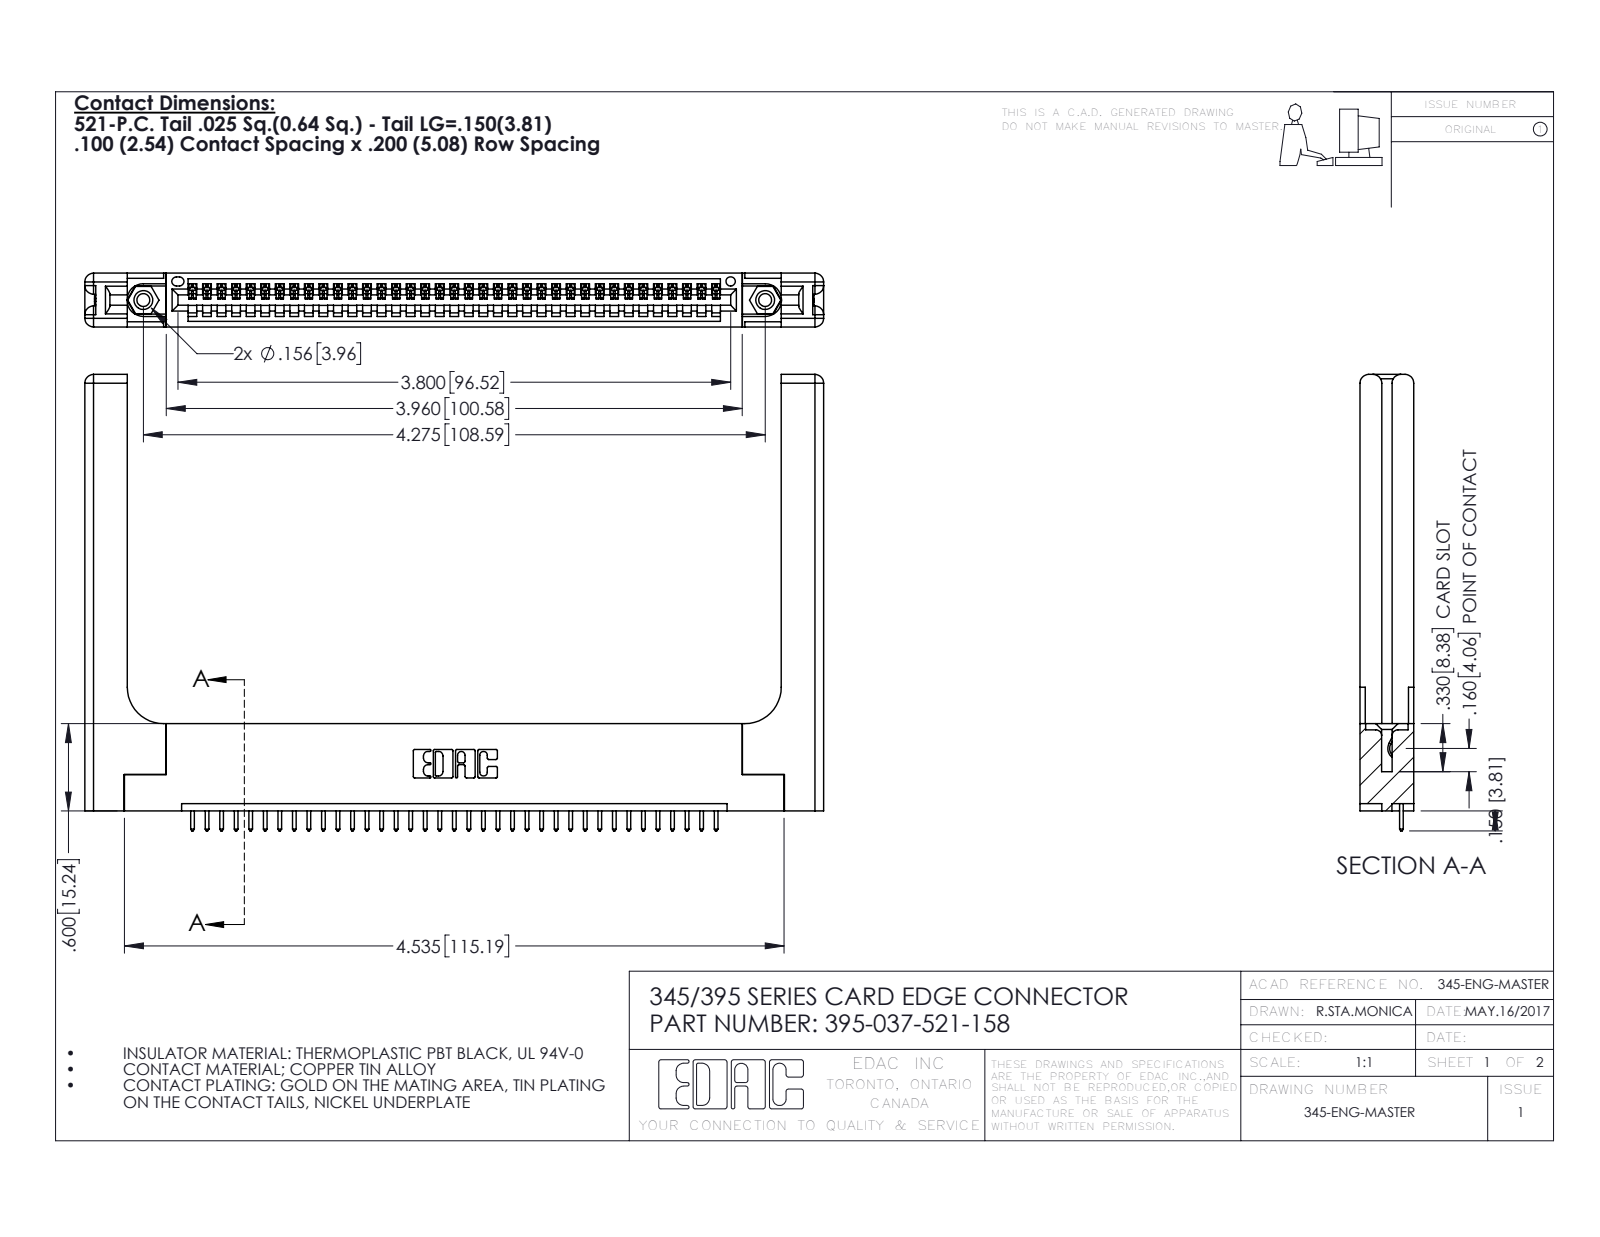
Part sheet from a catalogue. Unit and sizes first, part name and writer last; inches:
Units: inches
Overall size (bounding box): 5.079 × 3.137 × 0.37
Round holes (diameter × count): ⌀0.089 ×2, ⌀0.125 ×2, ⌀0.156 ×2, ⌀0.064 ×1
Round bosses / shafts (diameter × count): ⌀0.155 ×2
Partial cylindrical surfaces — rounded edges, fillets, slot ends (radius × count): R0.006 ×74, R0.01 ×74, R0.01 ×22, R0.06 ×16, R0.007 ×6, R0.031 ×6, R0.026 ×3, R0.03 ×2
Main face-to-face distances: 0.37, 0.072, 0.298, 0.2, 0.098, 0.272, 0.025, 0.148, 0.15, 0.225
Hole centre spacings: 0.27, 4.039, 4.275
Volume: 1.258 in³ · Surface area: 32.42 in²
Bodies: 42 solids, 2528 faces (1708 planar, 760 cylindrical, 60 other)
Part name (STEP PRODUCT): 345-220-058_345-220-058; 345 Part_Flush Mounting Lugs - 0.156 Dia-TH; 345-250-001_345-250-001-102; 345-292-001_345-293-121 (+1 more)
STEP written by: SolidWorks 2016 (CONFIG_CONTROL_DESIGN)
